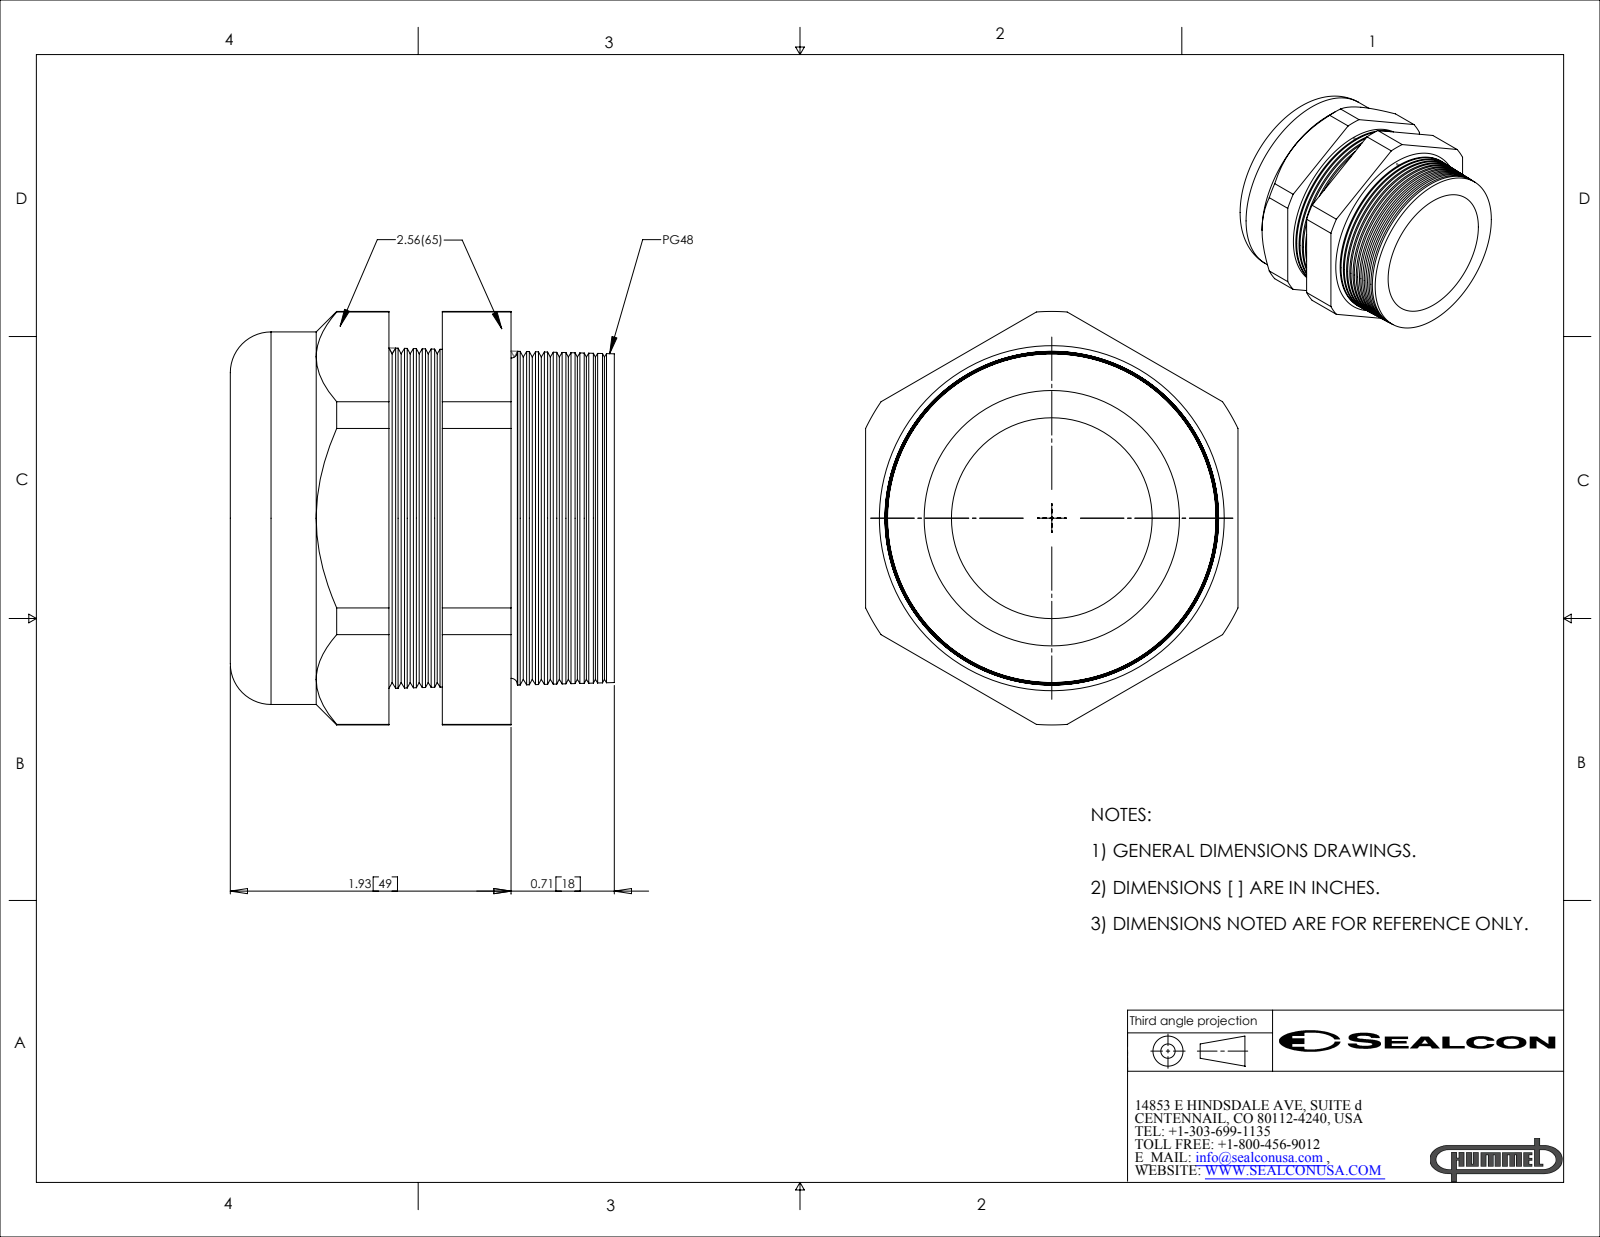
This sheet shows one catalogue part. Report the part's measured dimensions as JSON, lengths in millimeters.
{"part_name": "CD48CR-GY", "step_written_by": "SolidWorks 2007 (CONFIG_CONTROL_DESIGN)", "units": "millimeters", "bodies": {"solids": 2, "faces": 158, "planar": 20, "cylindrical": 22, "other": 116}, "overall_size": [72.2, 67.1, 65], "volume_mm3": 132100, "surface_area_mm2": 35590, "round_holes": [[35.1, 1], [44.6, 1]], "round_bosses_or_shafts": [[65, 1], [44.6, 1]], "partial_cylinders_radius": [[36.1, 1]], "face_to_face_distances": [65, 52.1, 22, 30, 12.7, 9.3, 39.4, 34, 21.3, 12]}
